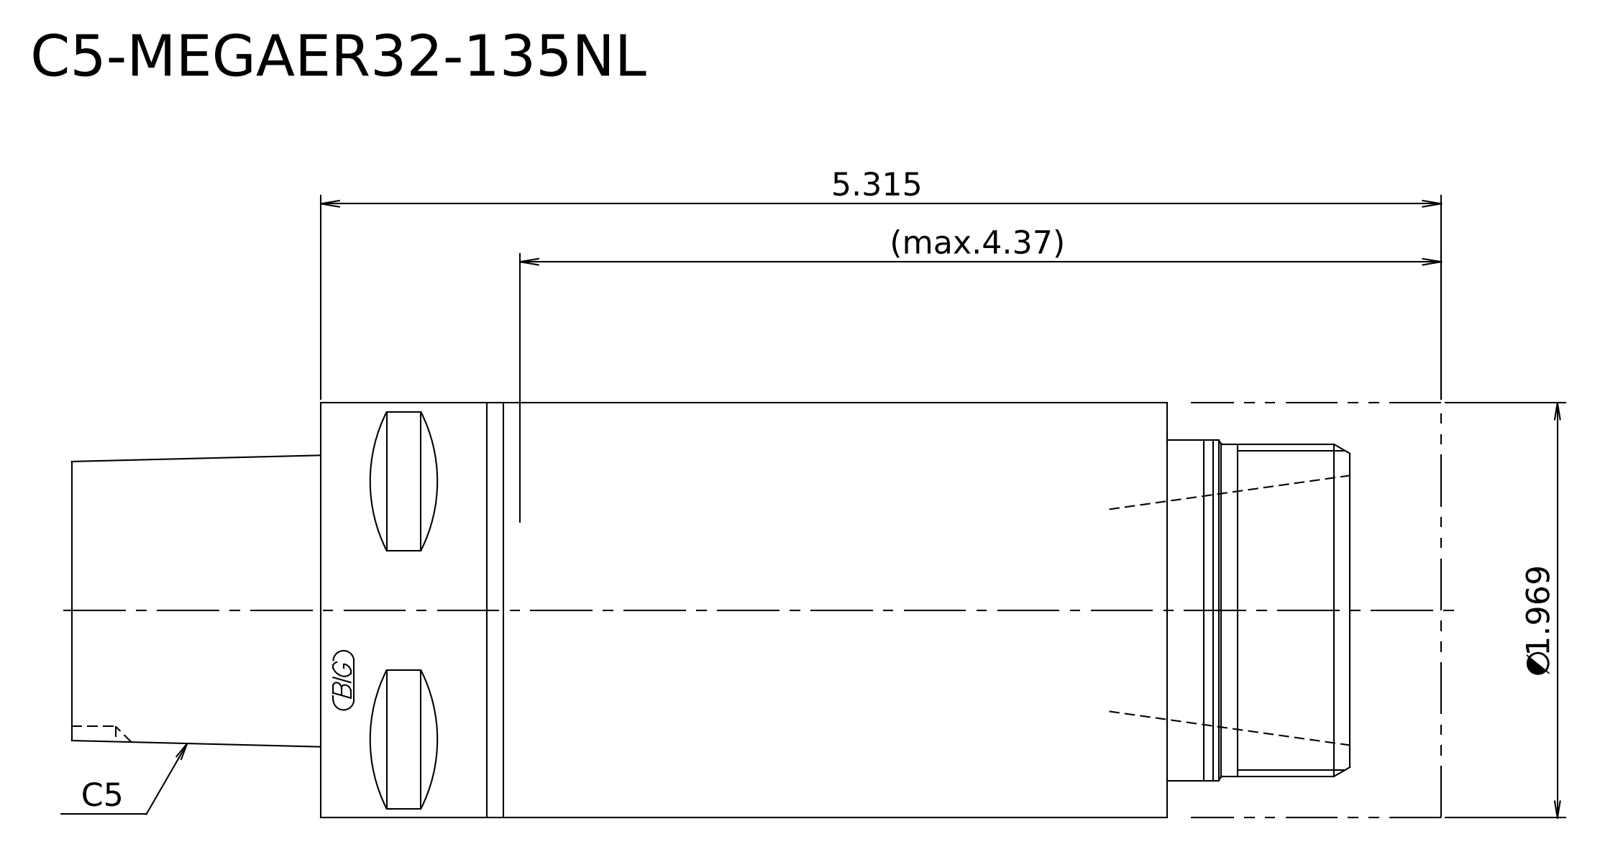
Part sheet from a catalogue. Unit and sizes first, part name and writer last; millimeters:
Units: millimetres
Overall size (bounding box): 165 × 50 × 50
Round bosses / shafts (diameter × count): ⌀50 ×1, ⌀41 ×1, ⌀40 ×1
Main face-to-face distances: 30.2, 11, 19.2, 135, 124, 104.8, 165, 154, 134.8, 30
Volume: 314 687 mm³ · Surface area: 34 434 mm²
Bodies: 2 solids, 13 faces (6 planar, 4 cylindrical, 3 other)
STEP written by: Kubotek KeyCreator 2011 V10.0.2 (22737) (automotive_design)
